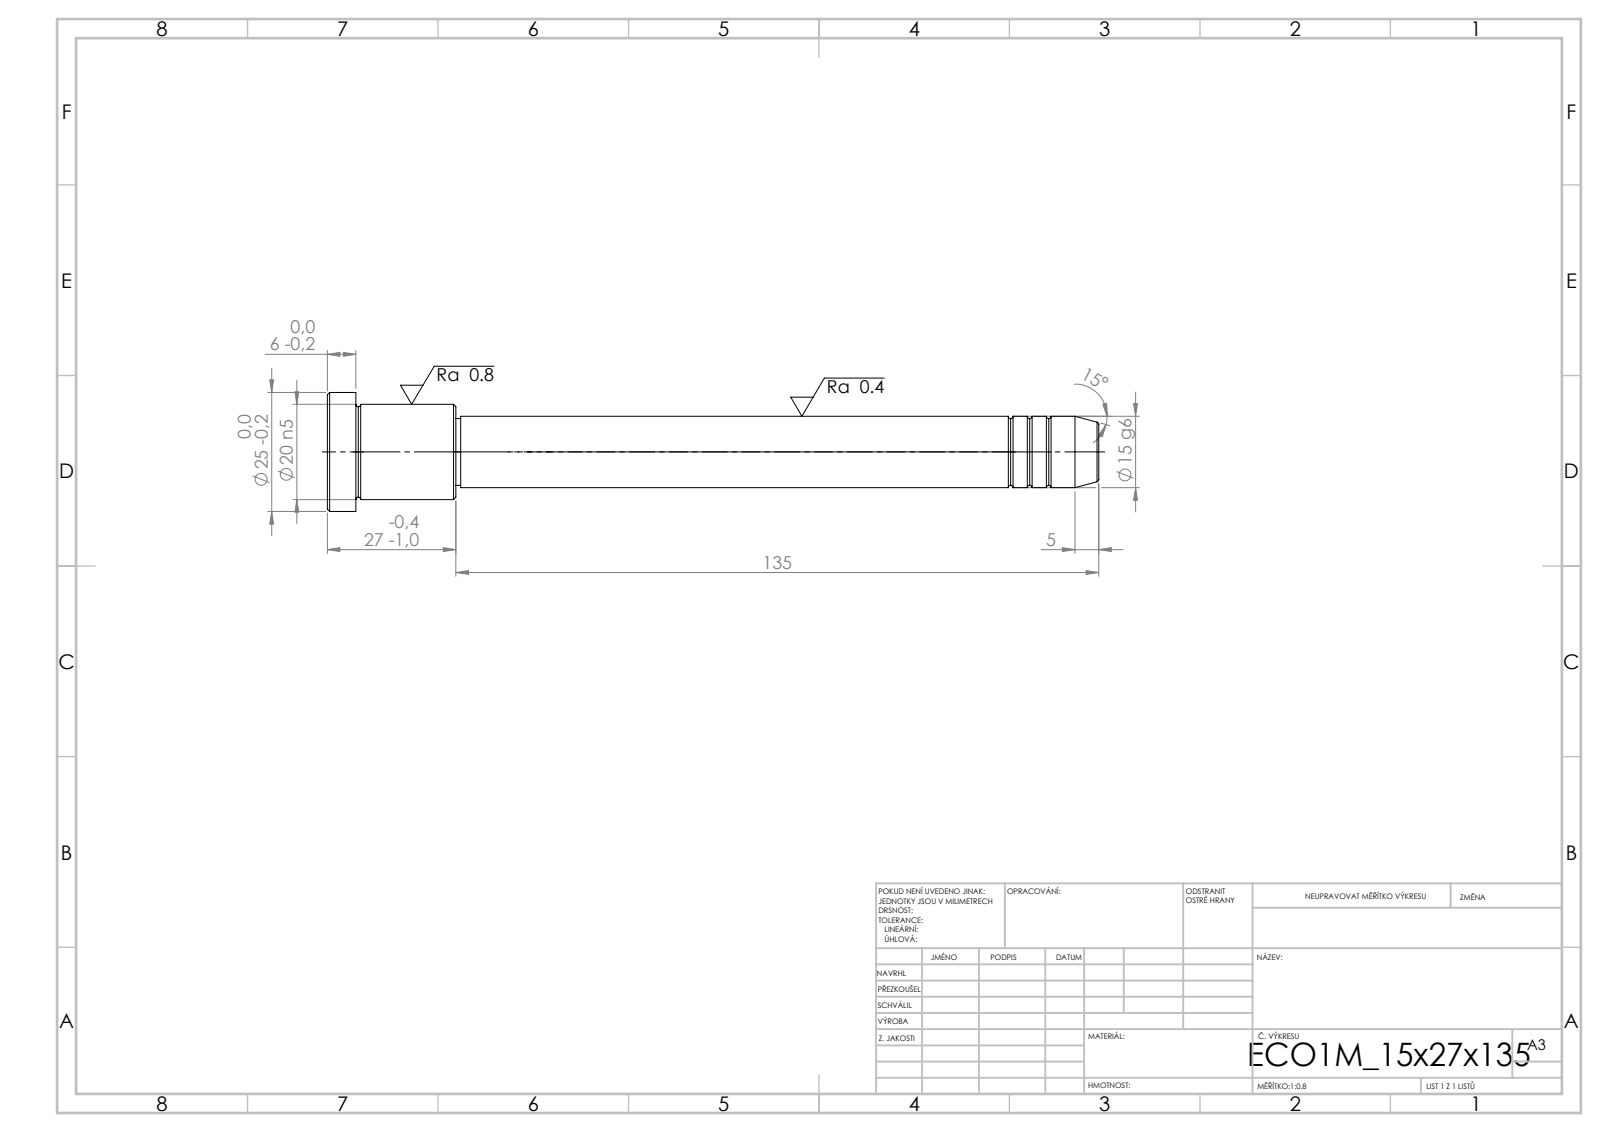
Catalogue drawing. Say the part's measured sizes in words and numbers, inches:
Its 3-D file was written by "SolidWorks 2019 (CONFIG_CONTROL_DESIGN)". It is 1 solid with 43 faces: 5 planar, 14 cylindrical and 24 other. Overall it measures 6.378 by 0.984 by 0.984 inches. Its volume is 2.022 cubic inches and its surface area 14.2 square inches. Round bosses or shafts: 1 of diameter 0.984, 1 of diameter 0.787, 1 of diameter 0.591, 1 of diameter 0.551. The main face-to-face distances are 0.236, 0.827, 1.063, 5.315, 6.142, 6.378, 5.276, 0.039, 0.866, 1.102.
